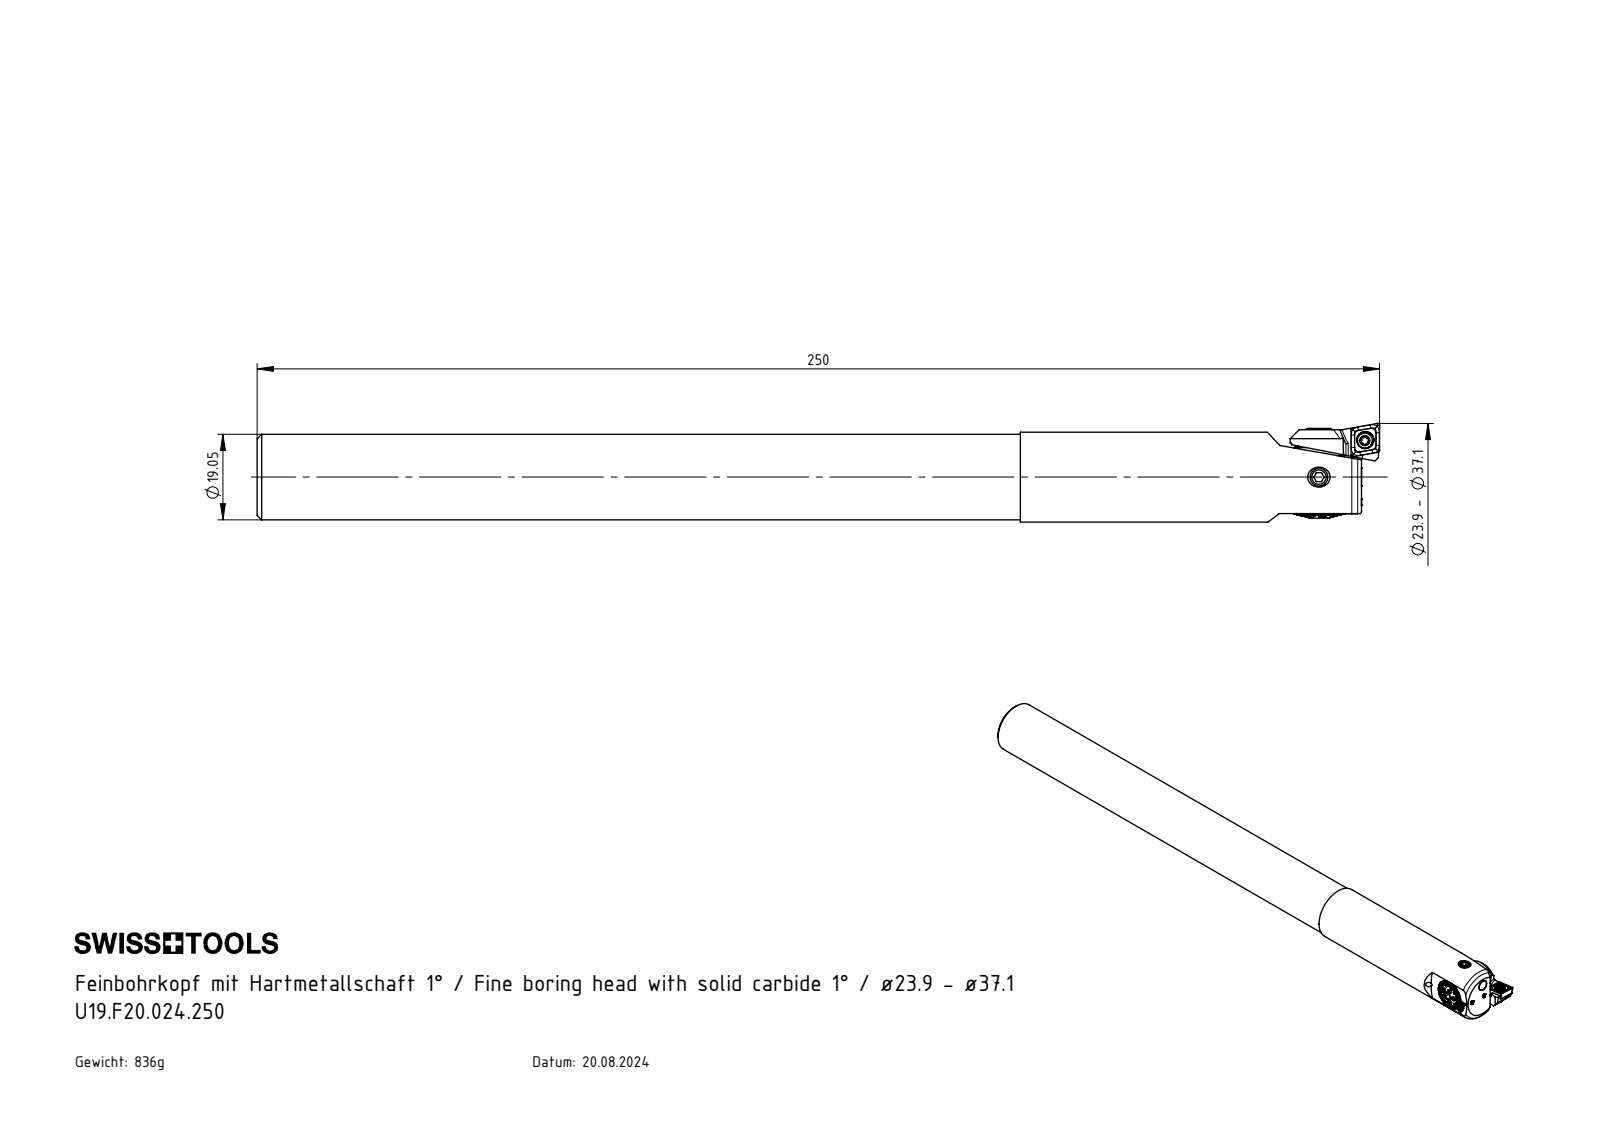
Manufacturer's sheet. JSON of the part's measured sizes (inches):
{"part_name": "ISO 8744-1.5x5; HP1-F20.K10.080_A; CCMT060204; F20-BG3.003.005_A (+8 more)", "step_written_by": "SolidWorks 2022 (AUTOMOTIVE_DESIGN)", "units": "inches", "bodies": {"solids": 16, "faces": 778, "planar": 340, "cylindrical": 152, "other": 286}, "overall_size": [9.843, 0.864, 0.787], "volume_in3": 4.175, "surface_area_in2": 36.39, "round_holes": [[0.055, 2], [0.13, 2], [0.02, 1], [0.059, 1], [0.079, 1], [0.081, 1], [0.11, 1], [0.148, 1], [0.152, 1], [0.157, 1], [0.165, 1], [0.177, 1]], "round_bosses_or_shafts": [[0.059, 3], [0.157, 2], [0.787, 1], [0.75, 1], [0.453, 1], [0.445, 1], [0.394, 1], [0.356, 1]], "partial_cylinders_radius": [[0.008, 6], [0.014, 4], [0.012, 2], [0.014, 2], [0.02, 2], [0.039, 2], [0.197, 2], [0.148, 1]], "face_to_face_distances": [6.693, 9.685, 2.992, 0.592, 0.039, 0.439, 0.153, 0.031, 0.11, 0.606], "hole_center_spacings": [0.03, 0.197, 0.22, 0.295]}
